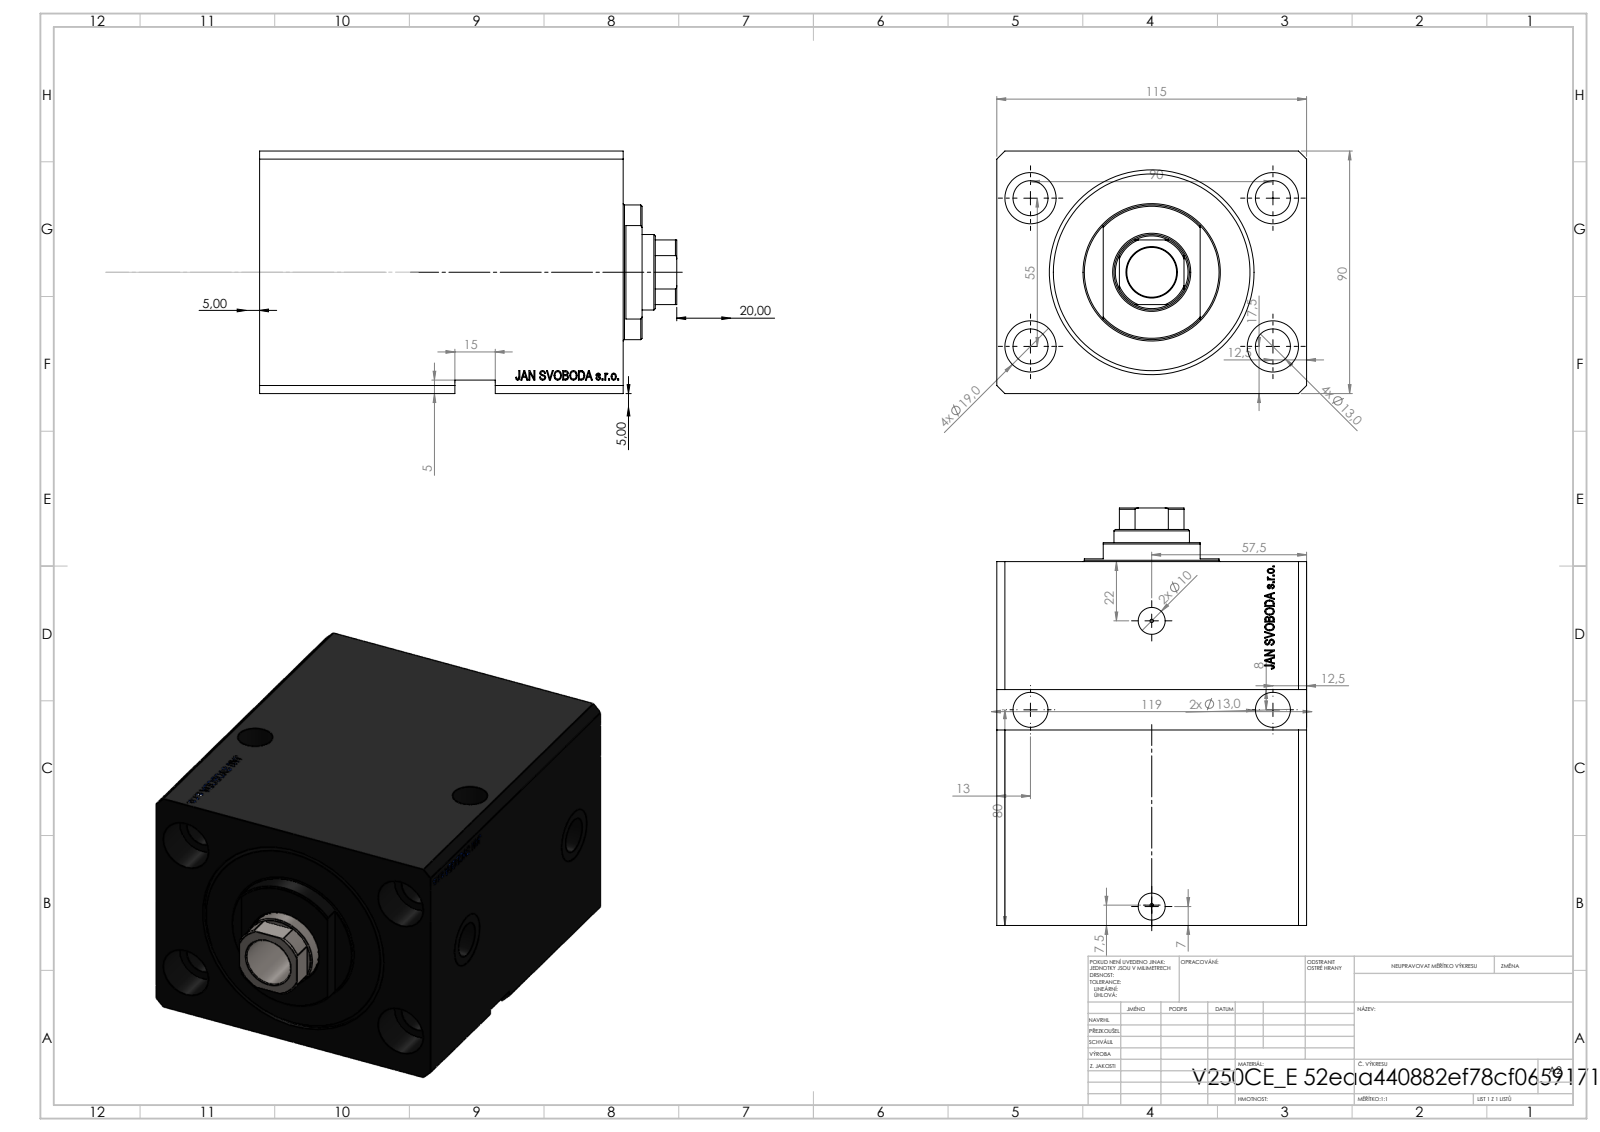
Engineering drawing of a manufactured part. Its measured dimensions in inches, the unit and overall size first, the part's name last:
Units: inches
Overall size (bounding box): 6.102 × 4.528 × 3.543
Round holes (diameter × count): ⌀0.512 ×8, ⌀0.049 ×4, ⌀0.748 ×4, ⌀0.394 ×2, ⌀0.518 ×2, ⌀0.787 ×2, ⌀0.728 ×1, ⌀1.102 ×1, ⌀2.48 ×1, ⌀2.992 ×1
Round bosses / shafts (diameter × count): ⌀1.969 ×1
Partial cylindrical surfaces — rounded edges, fillets, slot ends (radius × count): R0.531 ×1
Main face-to-face distances: 4.528, 3.543, 5.315, 0.705, 4.61, 0.787, 3.823, 2.559, 1.854, 1.969
Hole centre spacings: 2.076, 2.197, 3.376, 3.543, 1.575, 2.165, 2.185, 3.358
Volume: 69.81 in³ · Surface area: 269.5 in²
Bodies: 3 solids, 957 faces (467 planar, 104 cylindrical, 386 other)
Part name (STEP PRODUCT): V250CE_C_VCP; V250CE_E_Body; V250CE_VC_E
STEP written by: SolidWorks 2019 (CONFIG_CONTROL_DESIGN)
